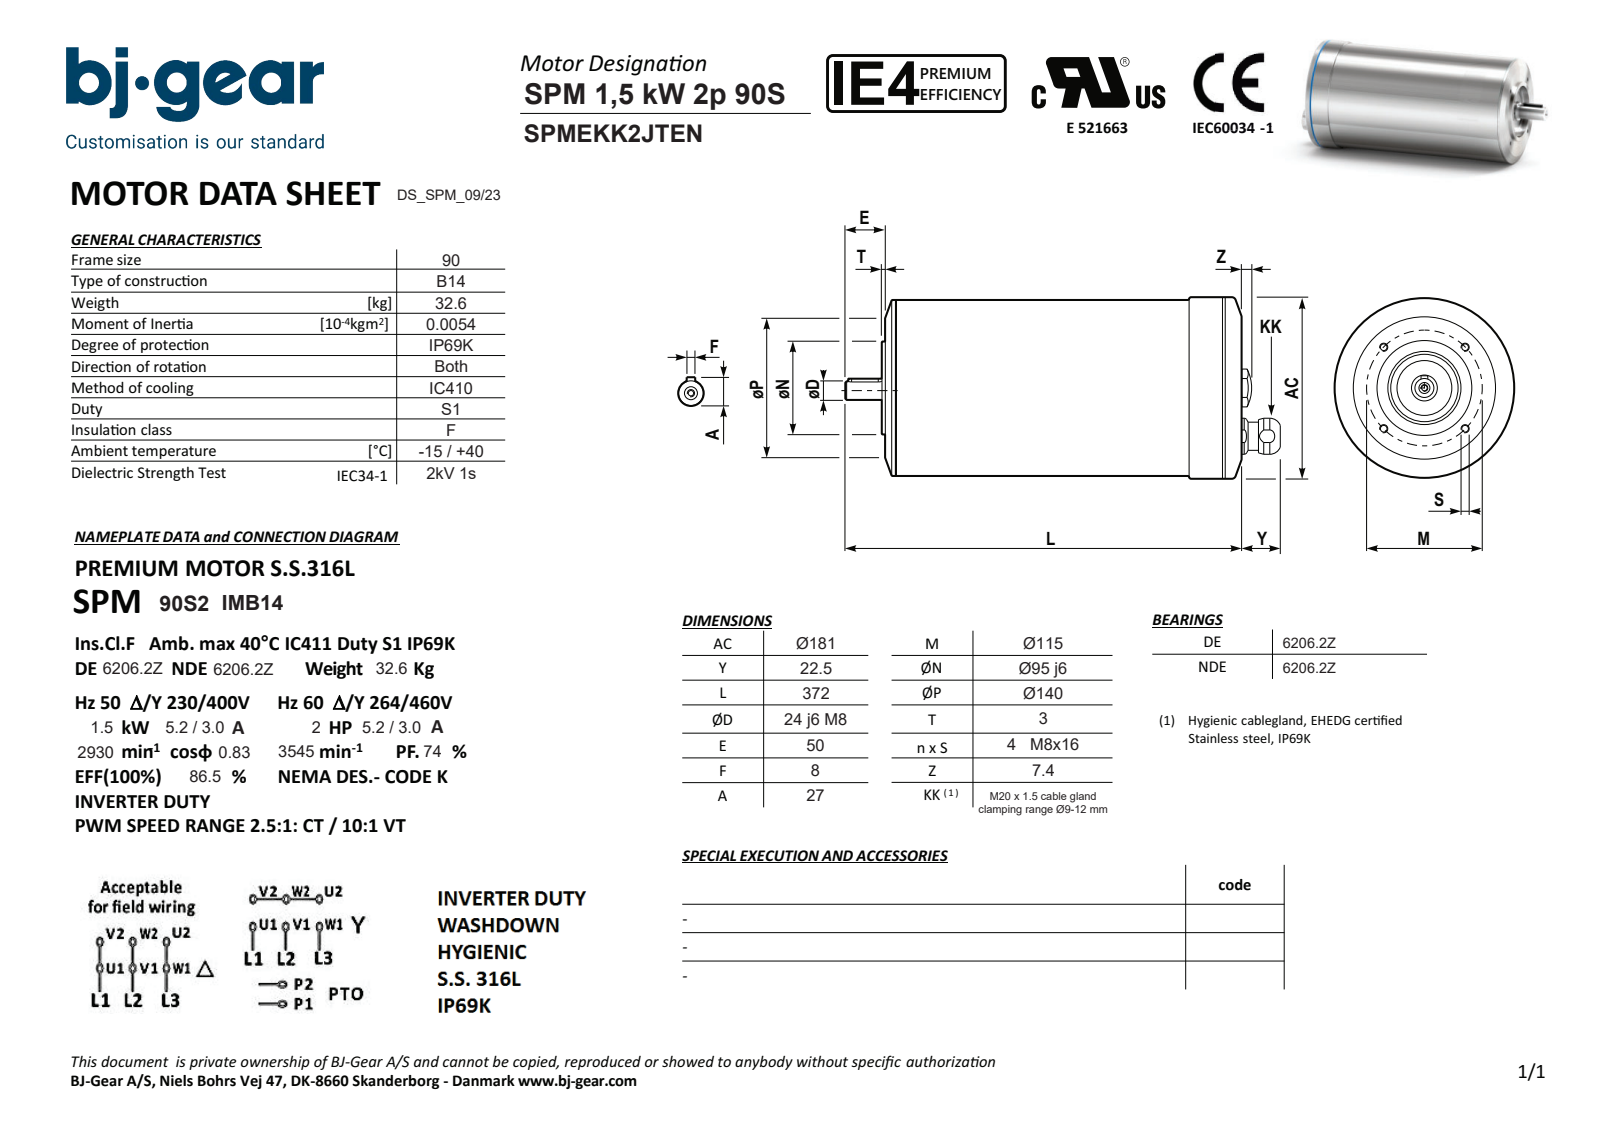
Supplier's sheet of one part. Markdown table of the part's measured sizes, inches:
| quantity | value |
| --- | --- |
| part name | SPMEKK2JTENN4KSA1-N---NNN |
| STEP written by | Solid Edge (AUTOMOTIVE_DESIGN) |
| units | inches |
| bodies | 1 solid, 87 faces (30 planar, 32 cylindrical, 25 other) |
| overall size | 15.728 × 7.126 × 7.126 |
| volume | 489 in³ |
| surface area | 369.9 in² |
| round holes (diameter × count) | 0.262 × 4, 0.194 × 1, 0.276 × 1, 0.331 × 1, 0.528 × 1, 3.346 × 1 |
| round bosses / shafts (diameter × count) | 7.126 × 1, 7.125 × 1, 7.008 × 1, 7.007 × 1, 3.74 × 1, 1.181 × 1, 0.945 × 1, 0.787 × 1 |
| partial cylindrical surfaces (radius × count) | 0.157 × 2, 0.504 × 1 |
| main face-to-face distances | 12.677, 0.236, 12.441, 12.795, 0.354, 0.118, 0.315, 0.945, 1.969, 14.646 |
| hole center spacings | 2.264, 3.202, 1.697, 4.092, 4.528, 2.165 |
